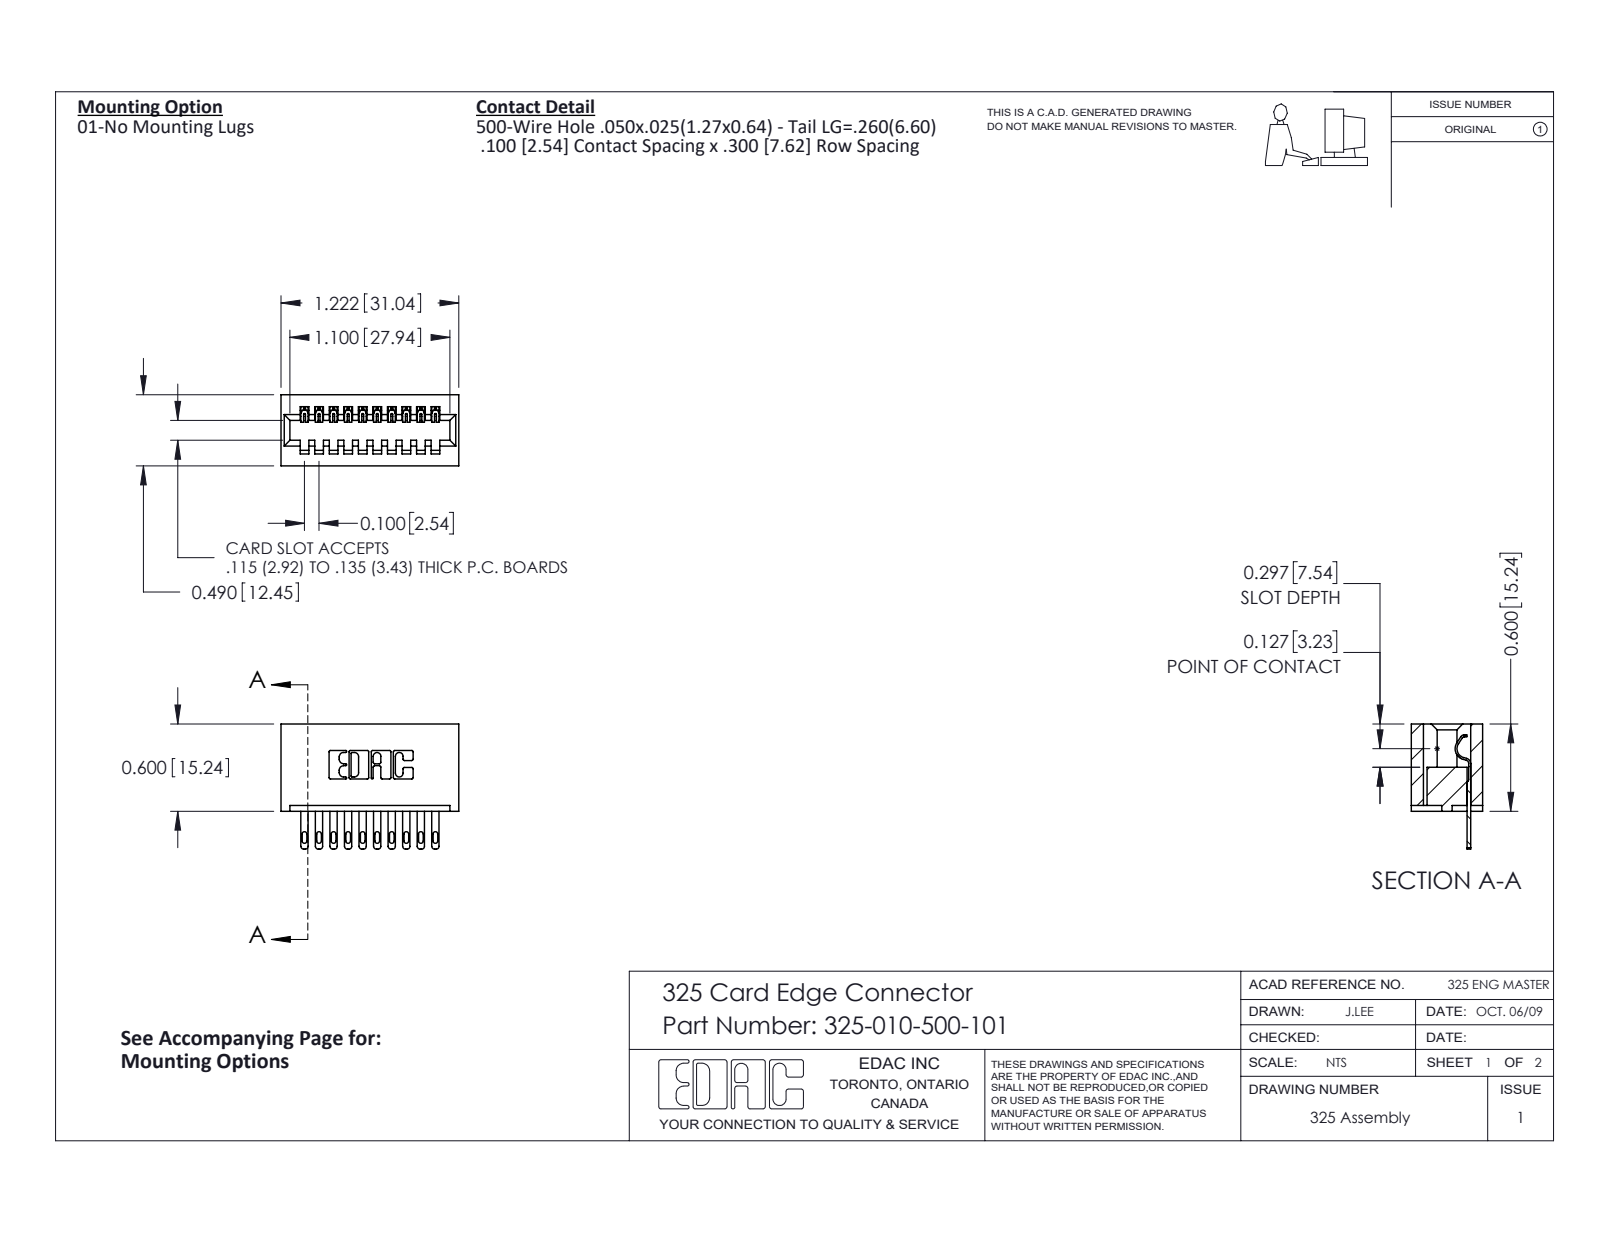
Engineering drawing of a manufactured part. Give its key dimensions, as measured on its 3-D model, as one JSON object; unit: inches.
{"part_name": "325 Part_Lugless; 325-010-500-101; 325-292-001_325-293-100", "step_written_by": "SolidWorks 2016 (CONFIG_CONTROL_DESIGN)", "units": "inches", "bodies": {"solids": 11, "faces": 646, "planar": 426, "cylindrical": 220, "other": 0}, "overall_size": [1.222, 0.86, 0.49], "volume_in3": 0.26, "surface_area_in2": 7.18, "partial_cylinders_radius": [[0.01, 22], [0.006, 20], [0.016, 20], [0.02, 20], [0.007, 6], [0.031, 6], [0.026, 3], [0.014, 1]], "face_to_face_distances": [0.3, 0.1, 0.083, 0.407, 0.2, 0.4, 0.49, 0.04, 0.6, 0.06]}
